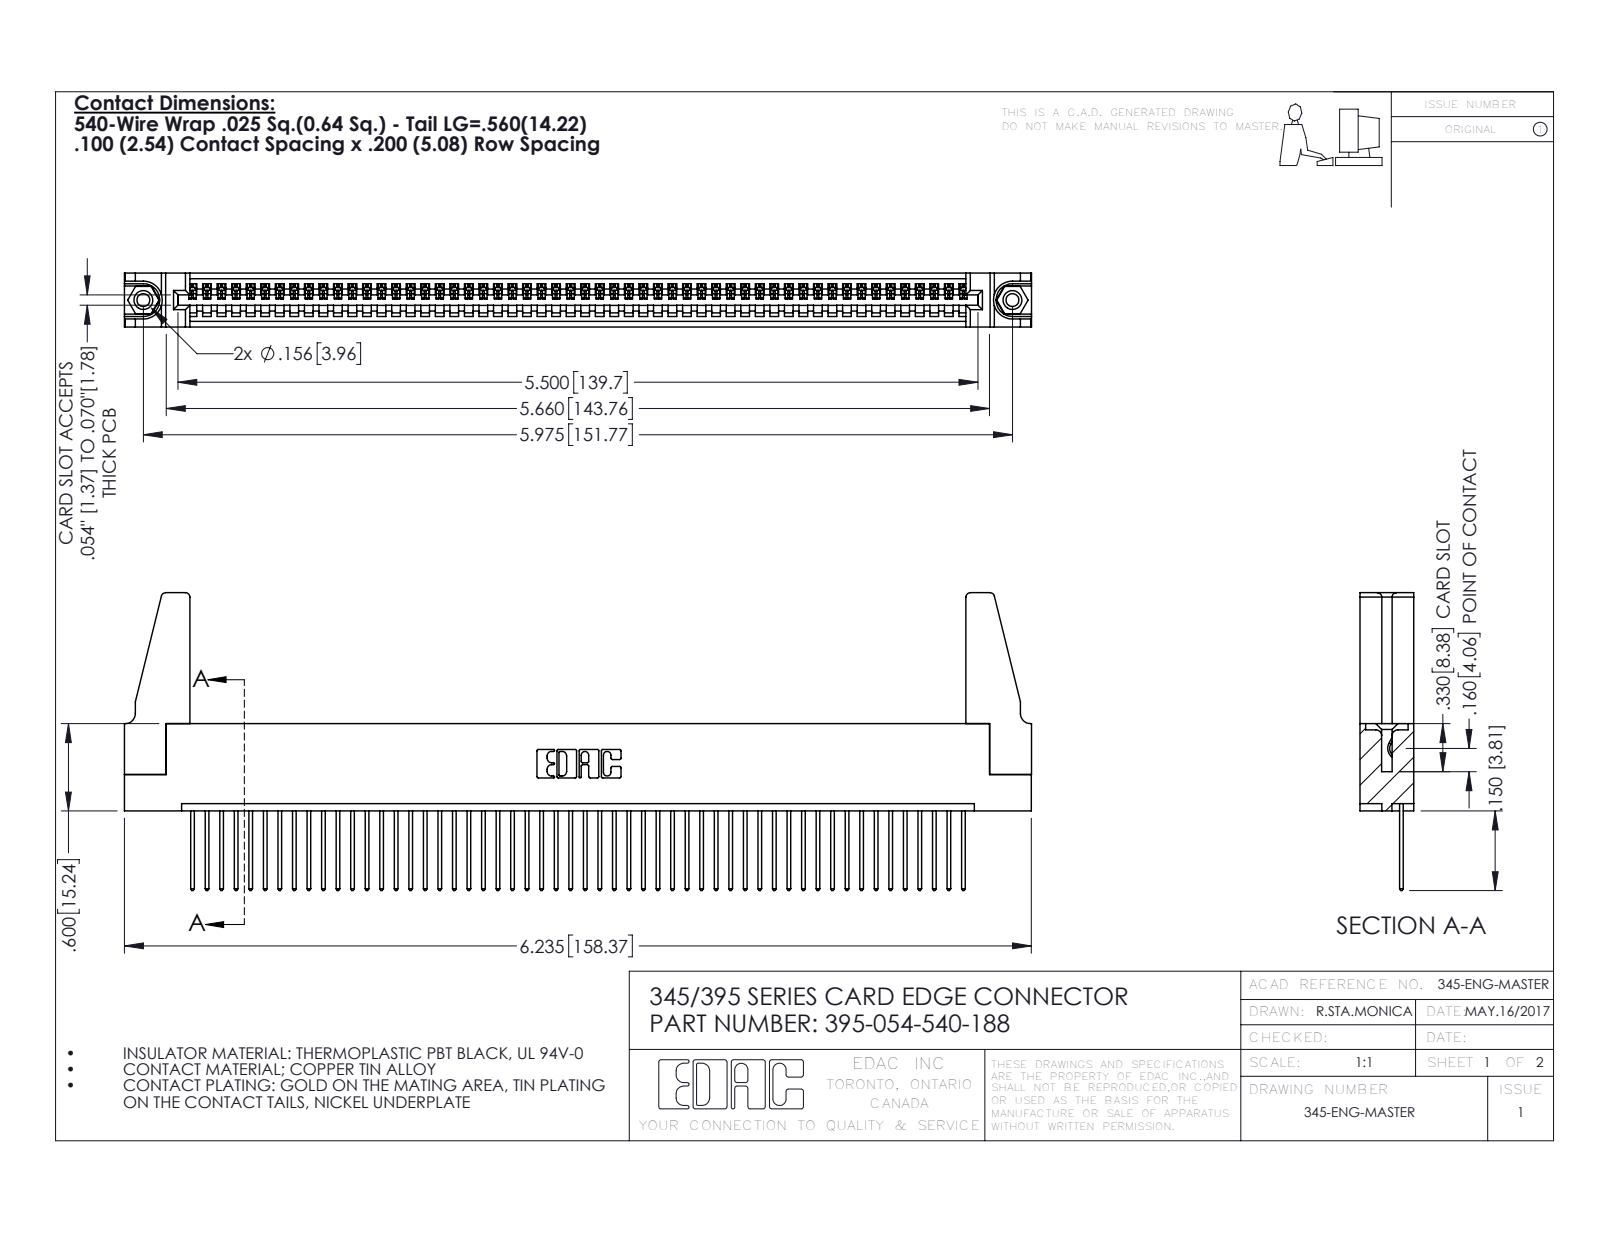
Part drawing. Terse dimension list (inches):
name: 345 Part_Flush Mounting Lugs - 0.156 Dia-TH; 345-250-001_345-250-001-102; 345-292-001_345-293-140; 395-054-540-188 (+1 more)
written by: SolidWorks 2016 (CONFIG_CONTROL_DESIGN)
unit: in
bodies: 59 solids, 3382 faces (2312 planar, 1054 cylindrical, 16 other)
size: 6.236 × 2.047 × 0.37
volume: 1.127 in³; area: 37.26 in²
holes: 2× ⌀0.089, 2× ⌀0.125, 2× ⌀0.156, 1× ⌀0.064
bosses: 2× ⌀0.155
rounds: 108× R0.006, 108× R0.01, 22× R0.01, 8× R0.03, 6× R0.007, 6× R0.031, 3× R0.026, 2× R0.031
face distances: 0.072, 0.298, 0.37, 0.098, 0.272, 0.025, 0.2, 0.225, 0.149, 0.072
hole spacings: 0.27, 5.739, 5.975
